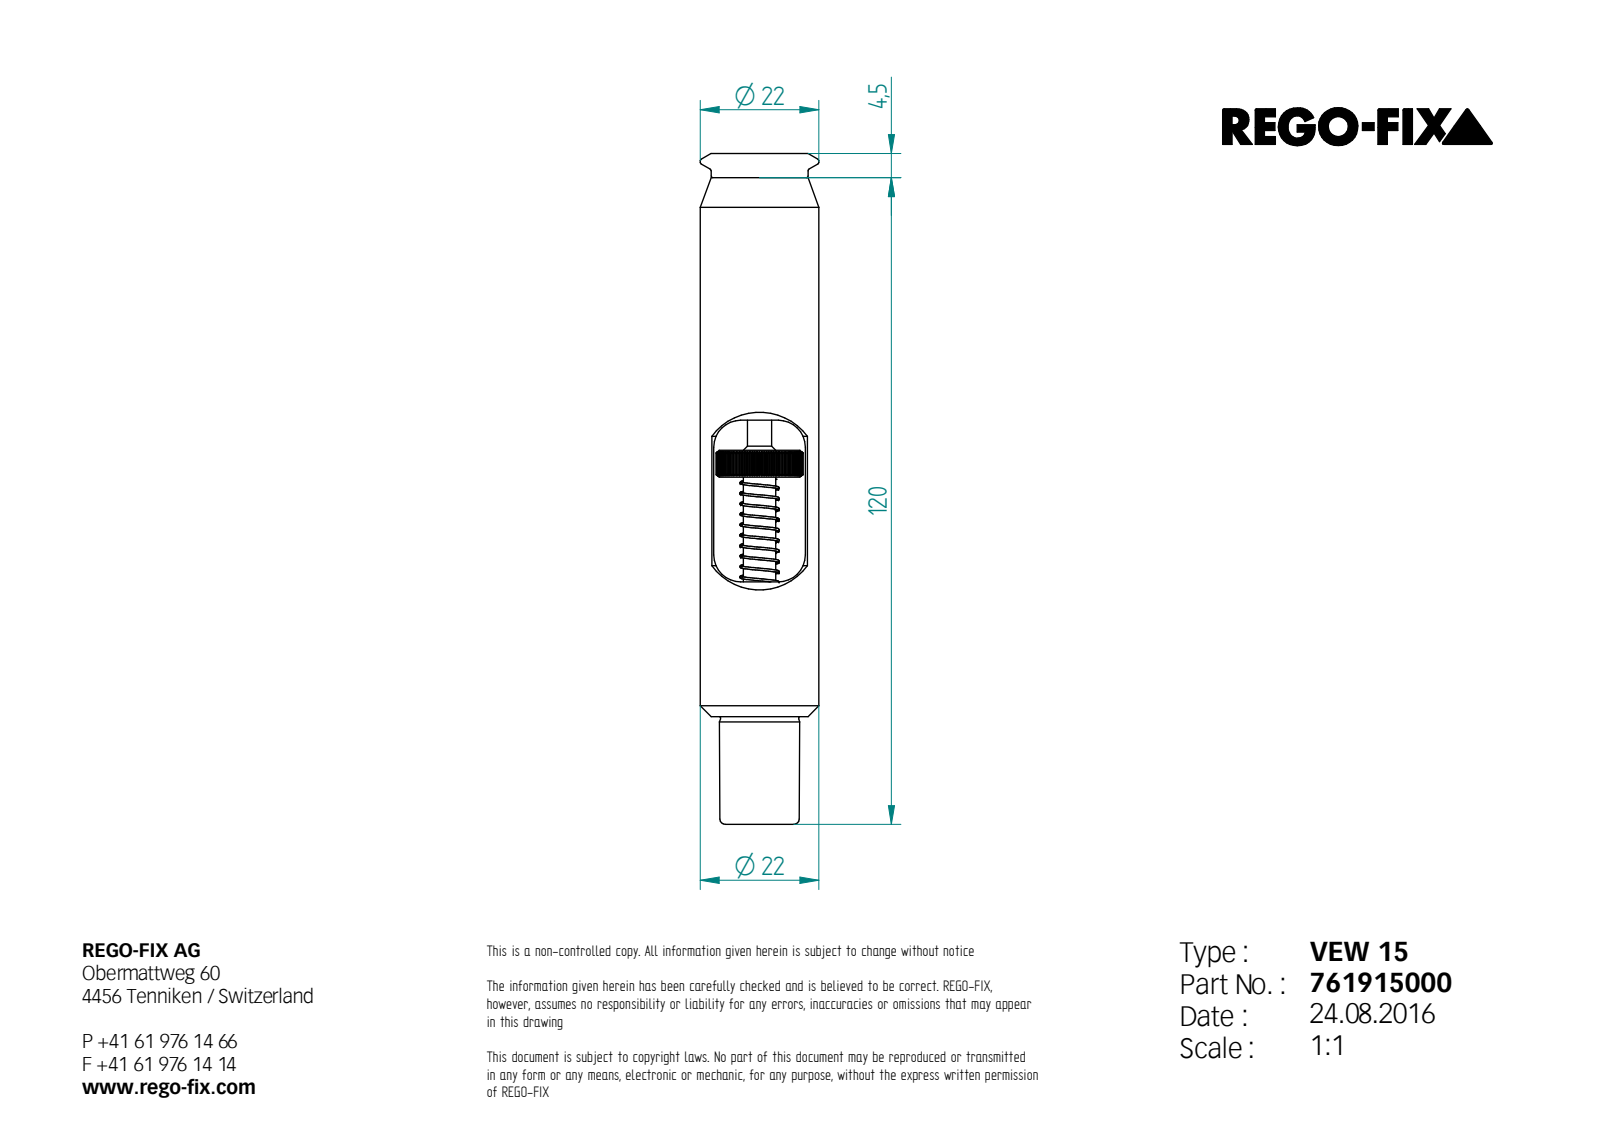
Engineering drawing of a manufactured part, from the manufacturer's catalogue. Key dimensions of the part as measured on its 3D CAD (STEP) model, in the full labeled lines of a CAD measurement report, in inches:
Part name (STEP PRODUCT): 0004320; 0007711; 0007744-oa0; 0007697 (+1 more)
STEP written by: Unknown (AUTOMOTIVE_DESIGN)
Units: inches
Bodies: 5 solids, 517 faces (336 planar, 162 cylindrical, 19 other)
Overall size (bounding box): 4.724 × 0.866 × 0.866
Volume: 1.469 in³ · Surface area: 20.58 in²
Round holes (diameter × count): ⌀0.194 ×1, ⌀0.24 ×1, ⌀0.283 ×1
Round bosses / shafts (diameter × count): ⌀0.866 ×1, ⌀0.236 ×1, ⌀0.177 ×1
Partial cylindrical surfaces — rounded edges, fillets, slot ends (radius × count): R0.197 ×4, R0.315 ×1
Main face-to-face distances: 0.669, 0.306, 0.197, 1.772, 0.766, 0.963, 2.953, 2.537, 2.734, 4.724
